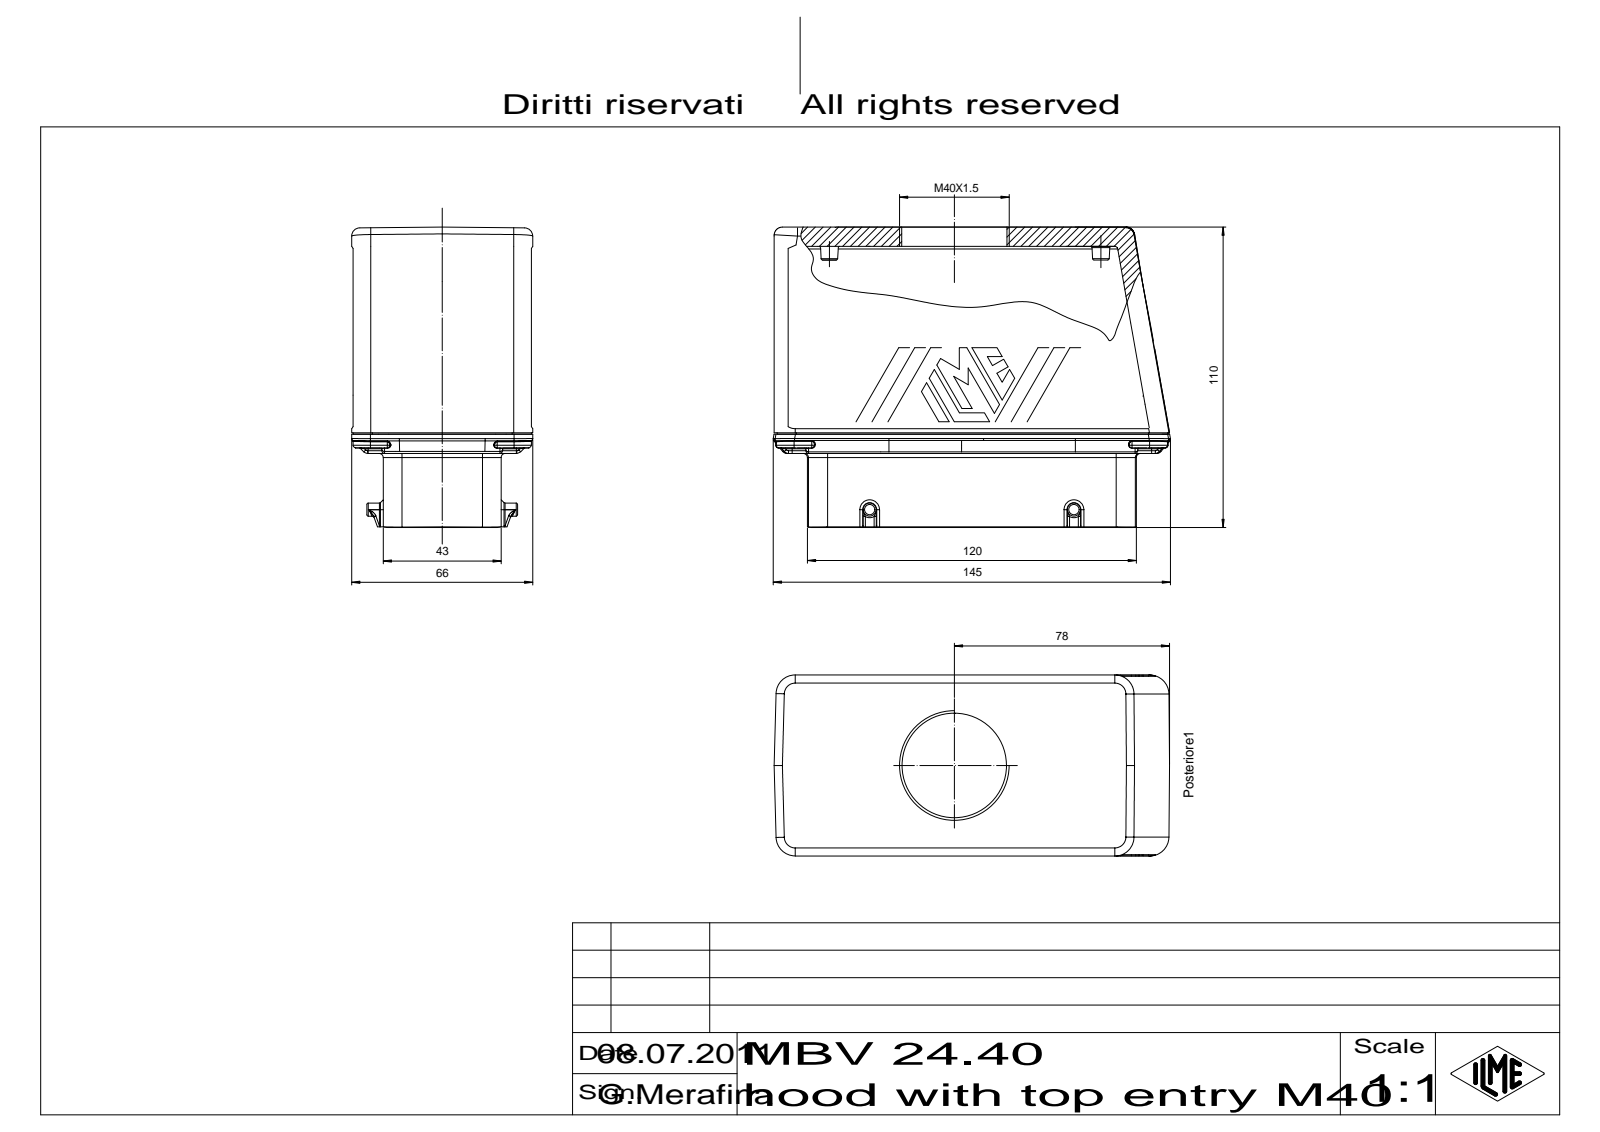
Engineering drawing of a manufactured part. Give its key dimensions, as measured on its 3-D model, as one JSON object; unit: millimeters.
{"part_name": "53848_Body_1", "step_written_by": "CoCreate Modeling 16.00A 16-Aug-2008 (C) Parametric Technology GmbH (AUTOMOTIVE_DESIGN)", "units": "millimeters", "bodies": {"solids": 1, "faces": 647, "planar": 333, "cylindrical": 150, "other": 164}, "overall_size": [117.26, 108.97, 66.01], "volume_mm3": 580000, "surface_area_mm2": 60054, "round_holes": [[40, 1]], "round_bosses_or_shafts": [[4.8, 2]], "partial_cylinders_radius": [[1, 44], [0.3, 18], [7, 12], [3, 10], [0.5, 8], [1.5, 6], [4.2, 4], [5, 4]], "face_to_face_distances": [65.01, 82.21, 0.4, 65.41, 11, 54.01, 54, 43, 11.01, 11.4]}
